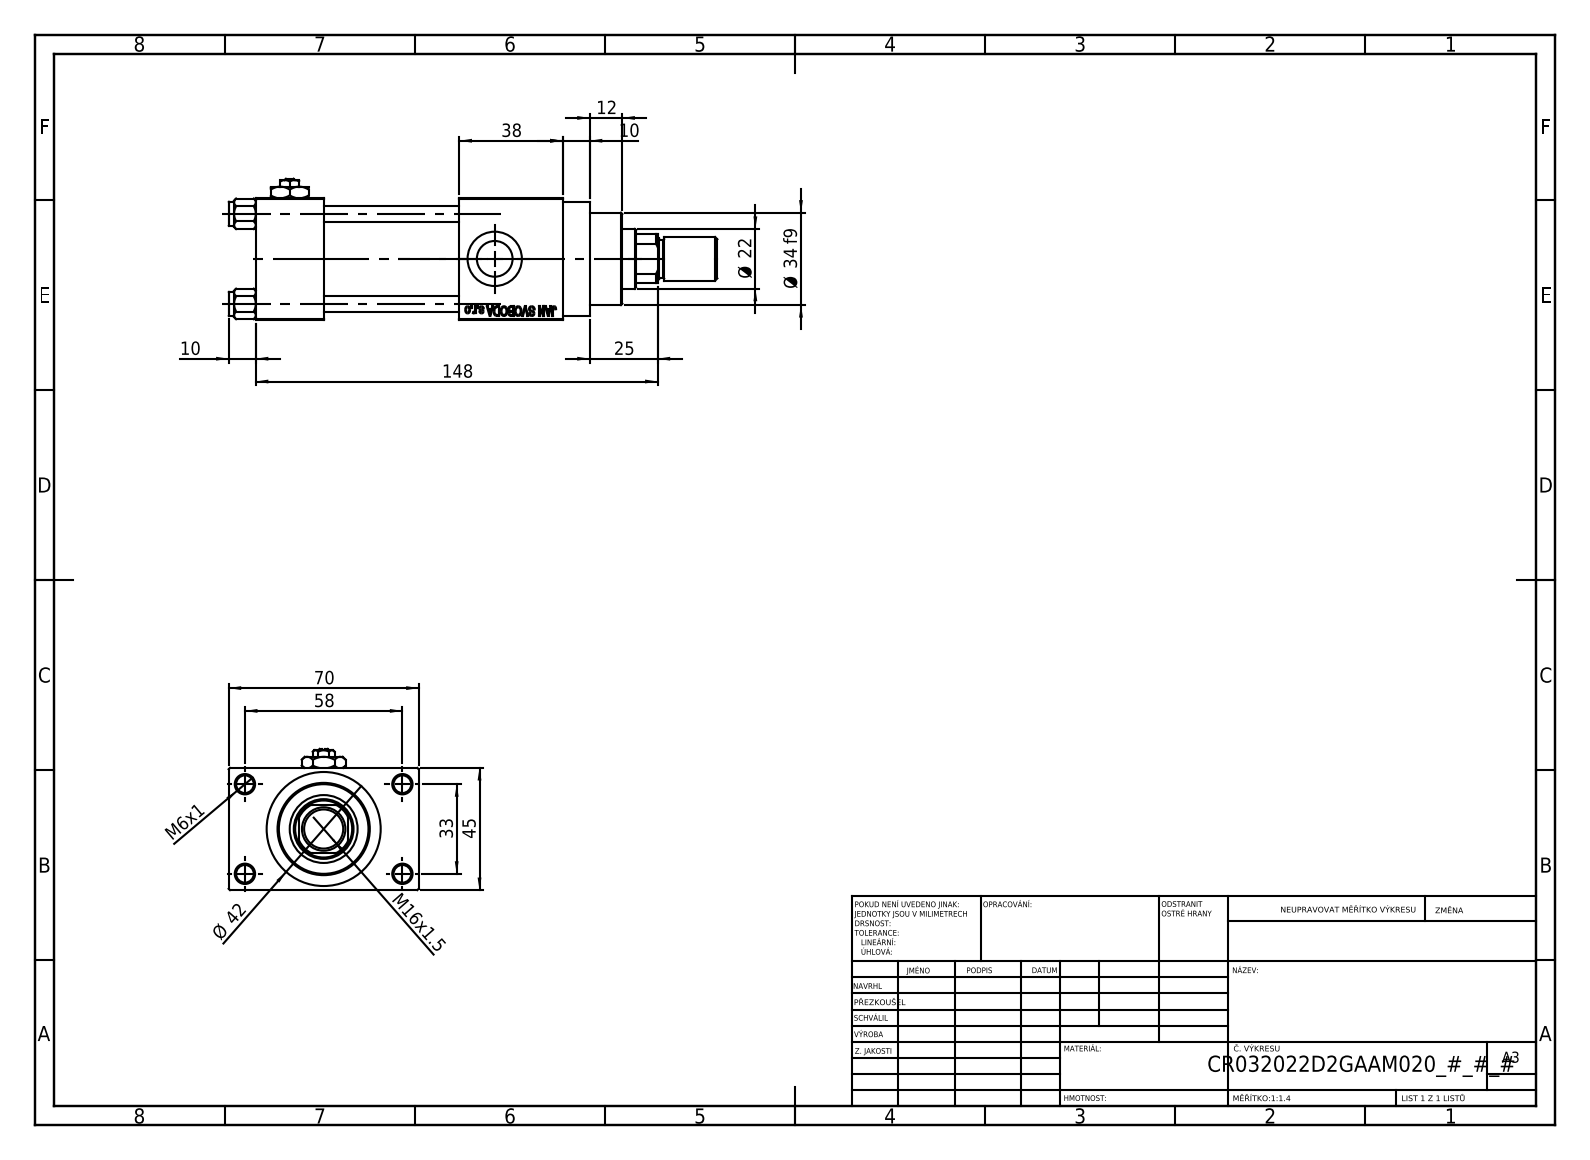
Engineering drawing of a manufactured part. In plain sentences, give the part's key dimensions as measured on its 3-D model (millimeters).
The part is named "ROD_END_AH; V215CR_VCP_D; NUT_M5_D; V215CR_D_TYCINKA (+3 more)". Its 3-D file was written by "SolidWorks 2019 (CONFIG_CONTROL_DESIGN)". It is 13 solids with 1159 faces: 522 planar, 93 cylindrical and 544 other. Overall it measures 180 by 70 by 52 millimeters. Its volume is 248 046 cubic millimeters and its surface area 82 109 square millimeters. Round holes: 4 of diameter 6, 4 of diameter 6.5, 2 of diameter 7, 2 of diameter 13.16, 2 of diameter 20, 1 of diameter 10.5, 1 of diameter 22, 1 of diameter 24, 1 of diameter 25, 1 of diameter 32, 1 of diameter 33. Round bosses or shafts: 4 of diameter 9, 1 of diameter 42, 1 of diameter 38, 1 of diameter 34, 1 of diameter 16, 1 of diameter 14. Partial cylindrical surfaces (rounded edges, fillets, slot ends): 1 of radius 10.5. The main face-to-face distances are 45, 25, 12.5, 57.5, 50, 75, 88, 38, 113, 70. The hole center spacings are 12.4, 23.48, 33.2, 33.37, 35.35, 45.6, 56.35, 33.
